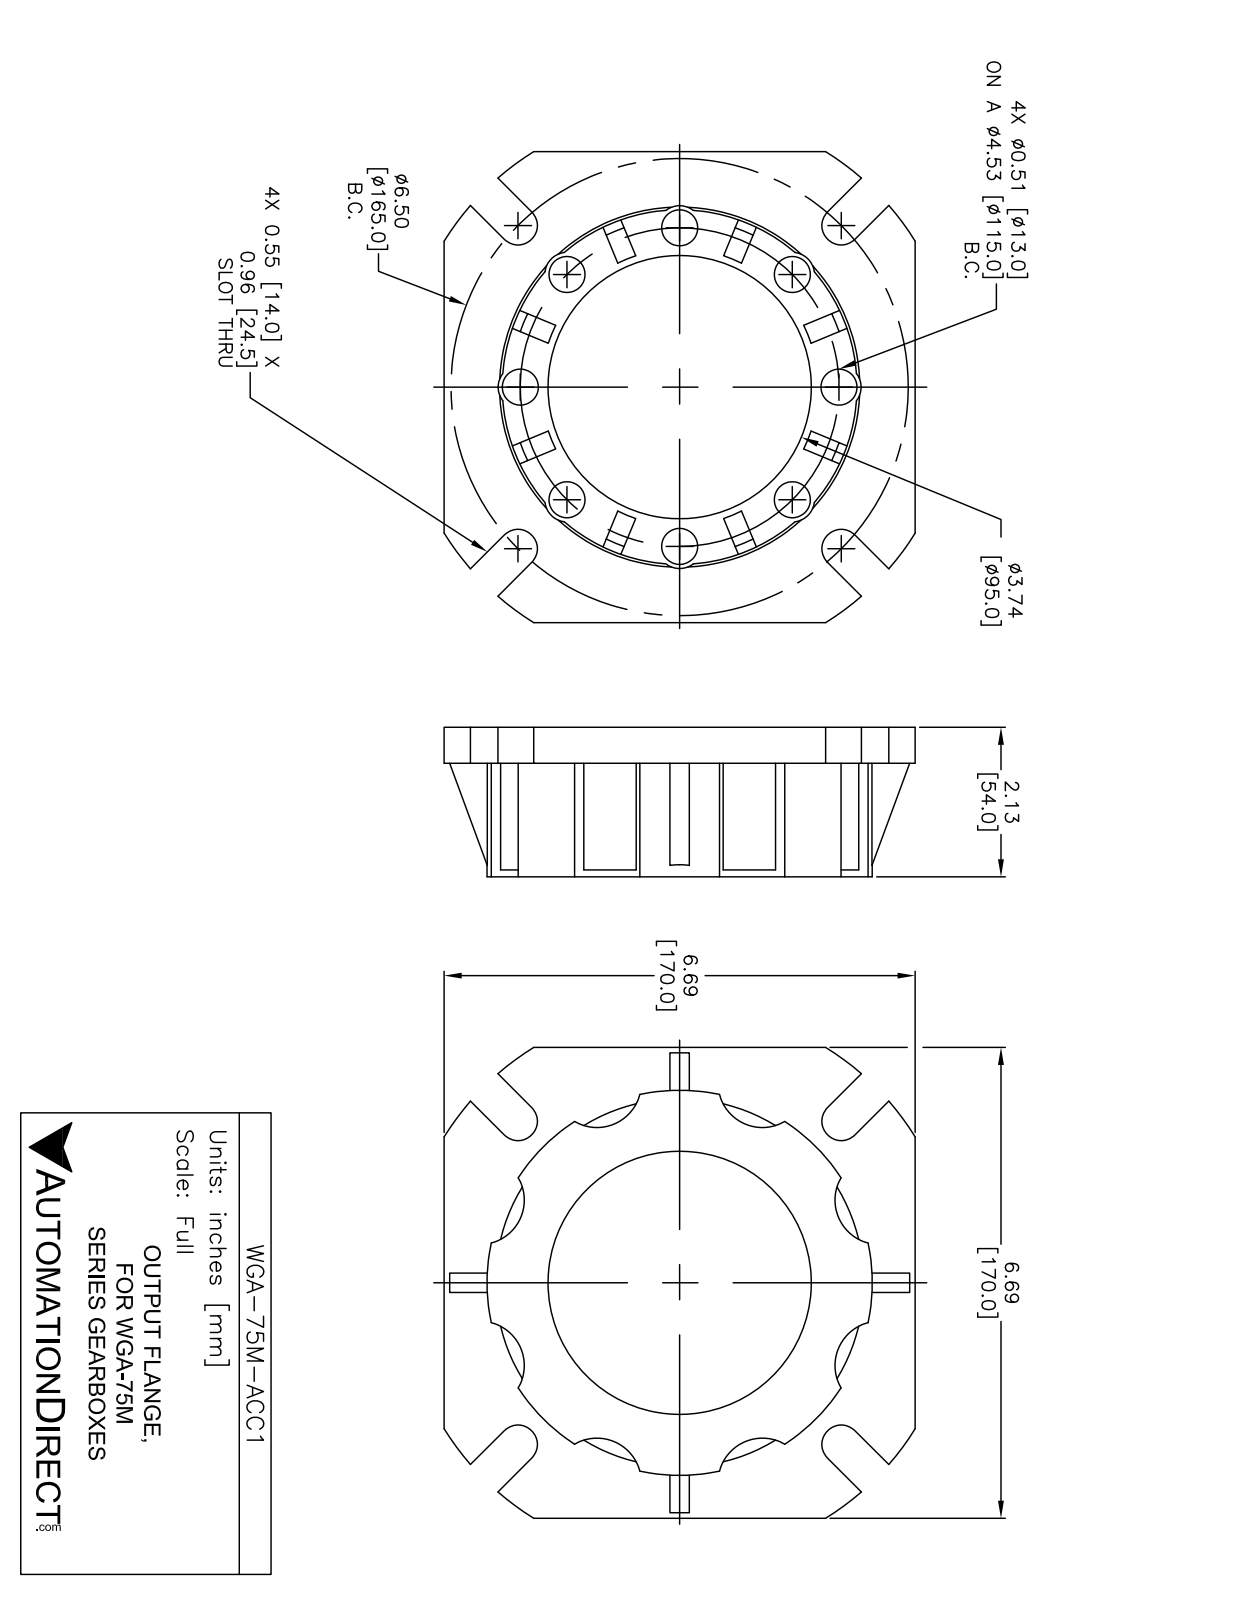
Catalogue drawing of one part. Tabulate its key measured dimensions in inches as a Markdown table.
| quantity | value |
| --- | --- |
| part name | WGA-75M-ACC1 |
| STEP written by | SolidWorks 2014 (AUTOMOTIVE_DESIGN) |
| units | inches |
| bodies | 1 solid, 168 faces (84 planar, 84 cylindrical, 0 other) |
| overall size | 6.693 × 6.693 × 2.126 |
| volume | 18.54 in³ |
| surface area | 147.8 in² |
| round holes (diameter × count) | 3.74 × 1, 5.039 × 1, 5.118 × 1 |
| round bosses / shafts (diameter × count) | 0.512 × 8 |
| partial cylindrical surfaces (radius × count) | 0.315 × 8, 0.63 × 8, 0.276 × 4, 2.618 × 1, 2.736 × 1, 3.937 × 1 |
| main face-to-face distances | 0.512, 0.276, 1.614, 2.126, 1.339, 1.85, 6.693, 3.209, 3.484, 0.591 |
